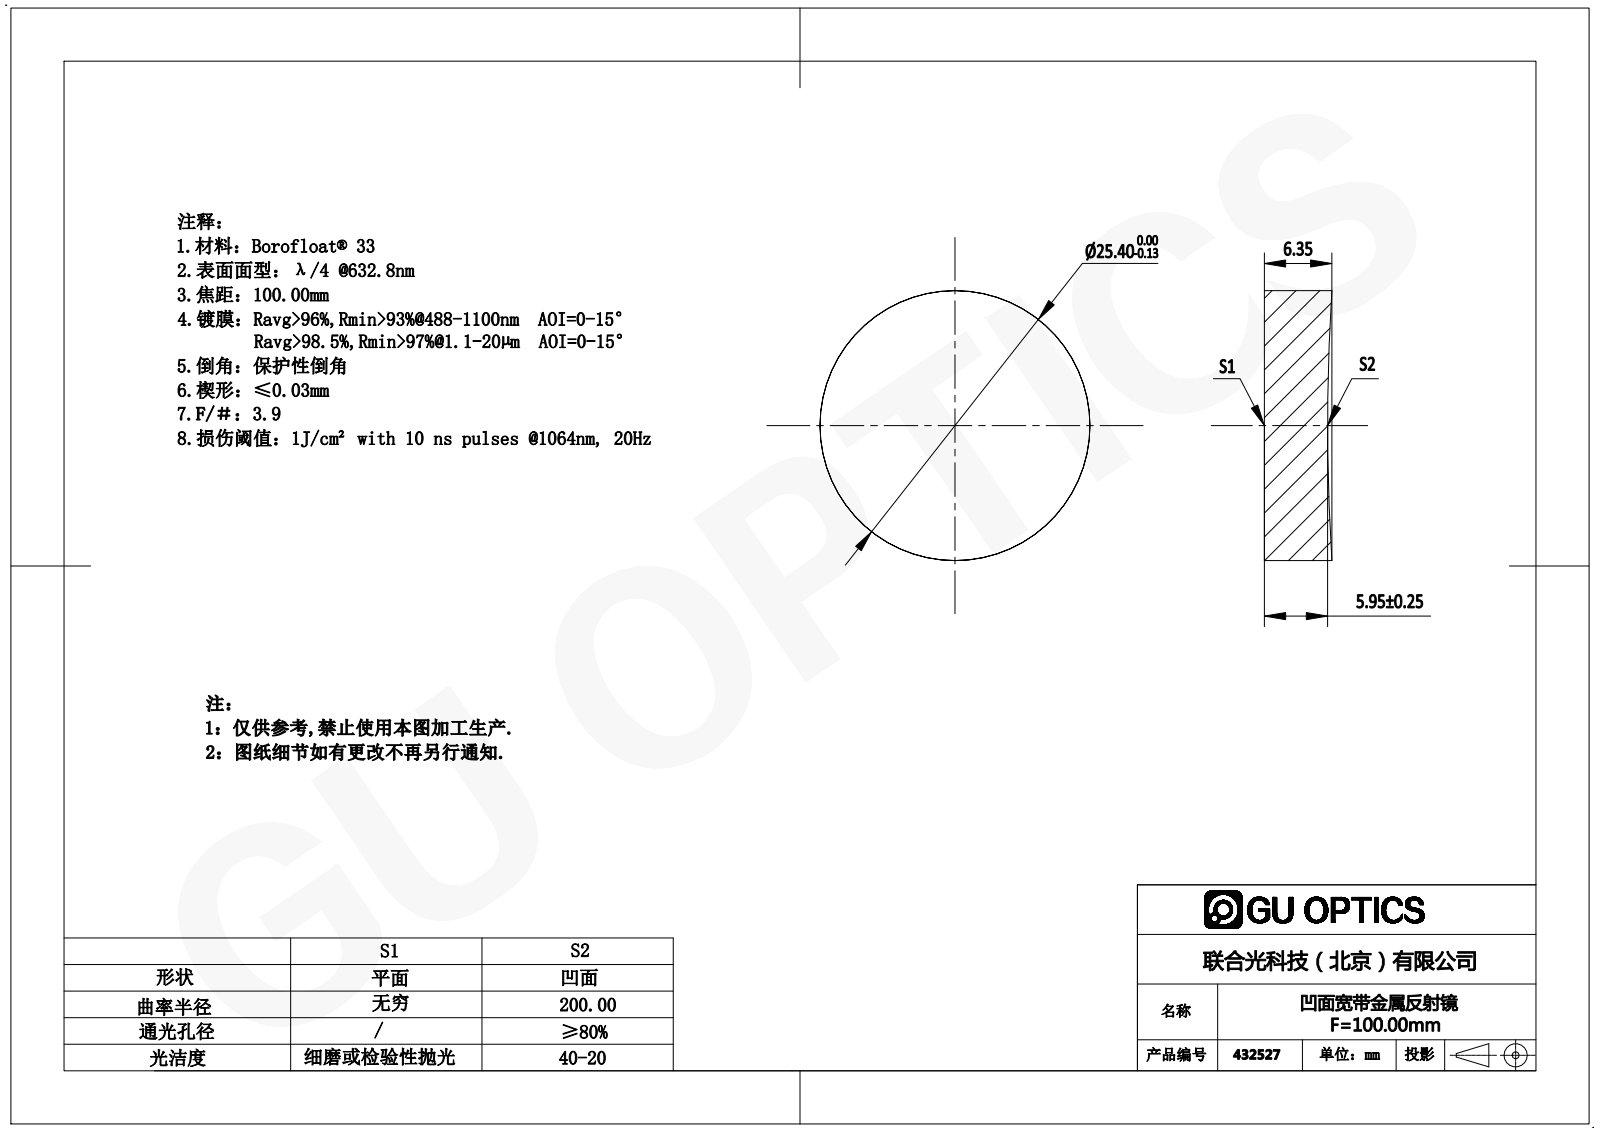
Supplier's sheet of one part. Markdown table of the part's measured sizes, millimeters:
| quantity | value |
| --- | --- |
| part name | 432517 |
| STEP written by | SolidWorks 2016 (AUTOMOTIVE_DESIGN) |
| units | millimeters |
| bodies | 1 solid, 5 faces (1 planar, 2 cylindrical, 2 other) |
| overall size | 25.4 × 25.4 × 6.35 |
| volume | 3 117 mm³ |
| surface area | 1 521 mm² |
| round bosses / shafts (diameter × count) | 25.4 × 1 |
